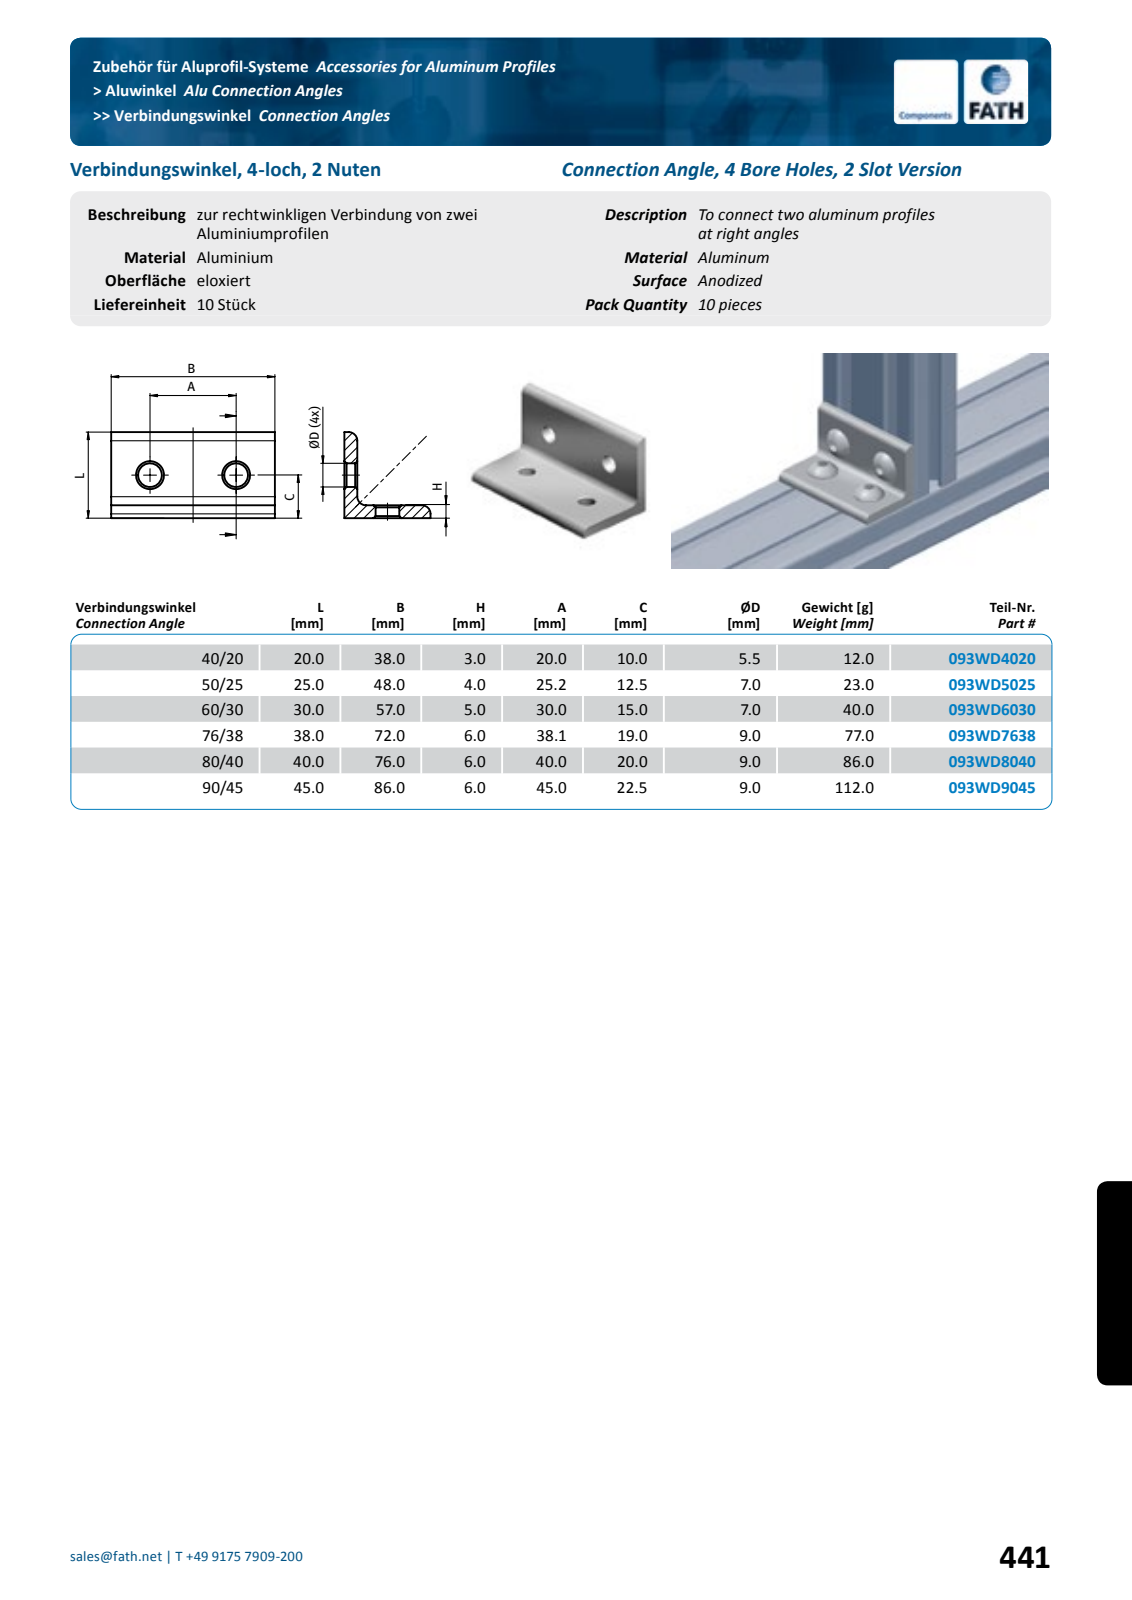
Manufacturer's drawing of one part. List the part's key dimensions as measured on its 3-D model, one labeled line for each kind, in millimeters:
Part name (STEP PRODUCT): fath_093wd6030
STEP written by: Spatial InterOp 3D (automotive_design)
Units: millimetres
Bodies: 1 solid, 35 faces (8 planar, 11 cylindrical, 16 other)
Overall size (bounding box): 57 × 30 × 30
Volume: 14 772 mm³ · Surface area: 7 249 mm²
Round holes (diameter × count): ⌀7 ×4
Partial cylindrical surfaces — rounded edges, fillets, slot ends (radius × count): R3 ×3
Main face-to-face distances: 5, 57, 30, 25
Hole centre spacings: 30
